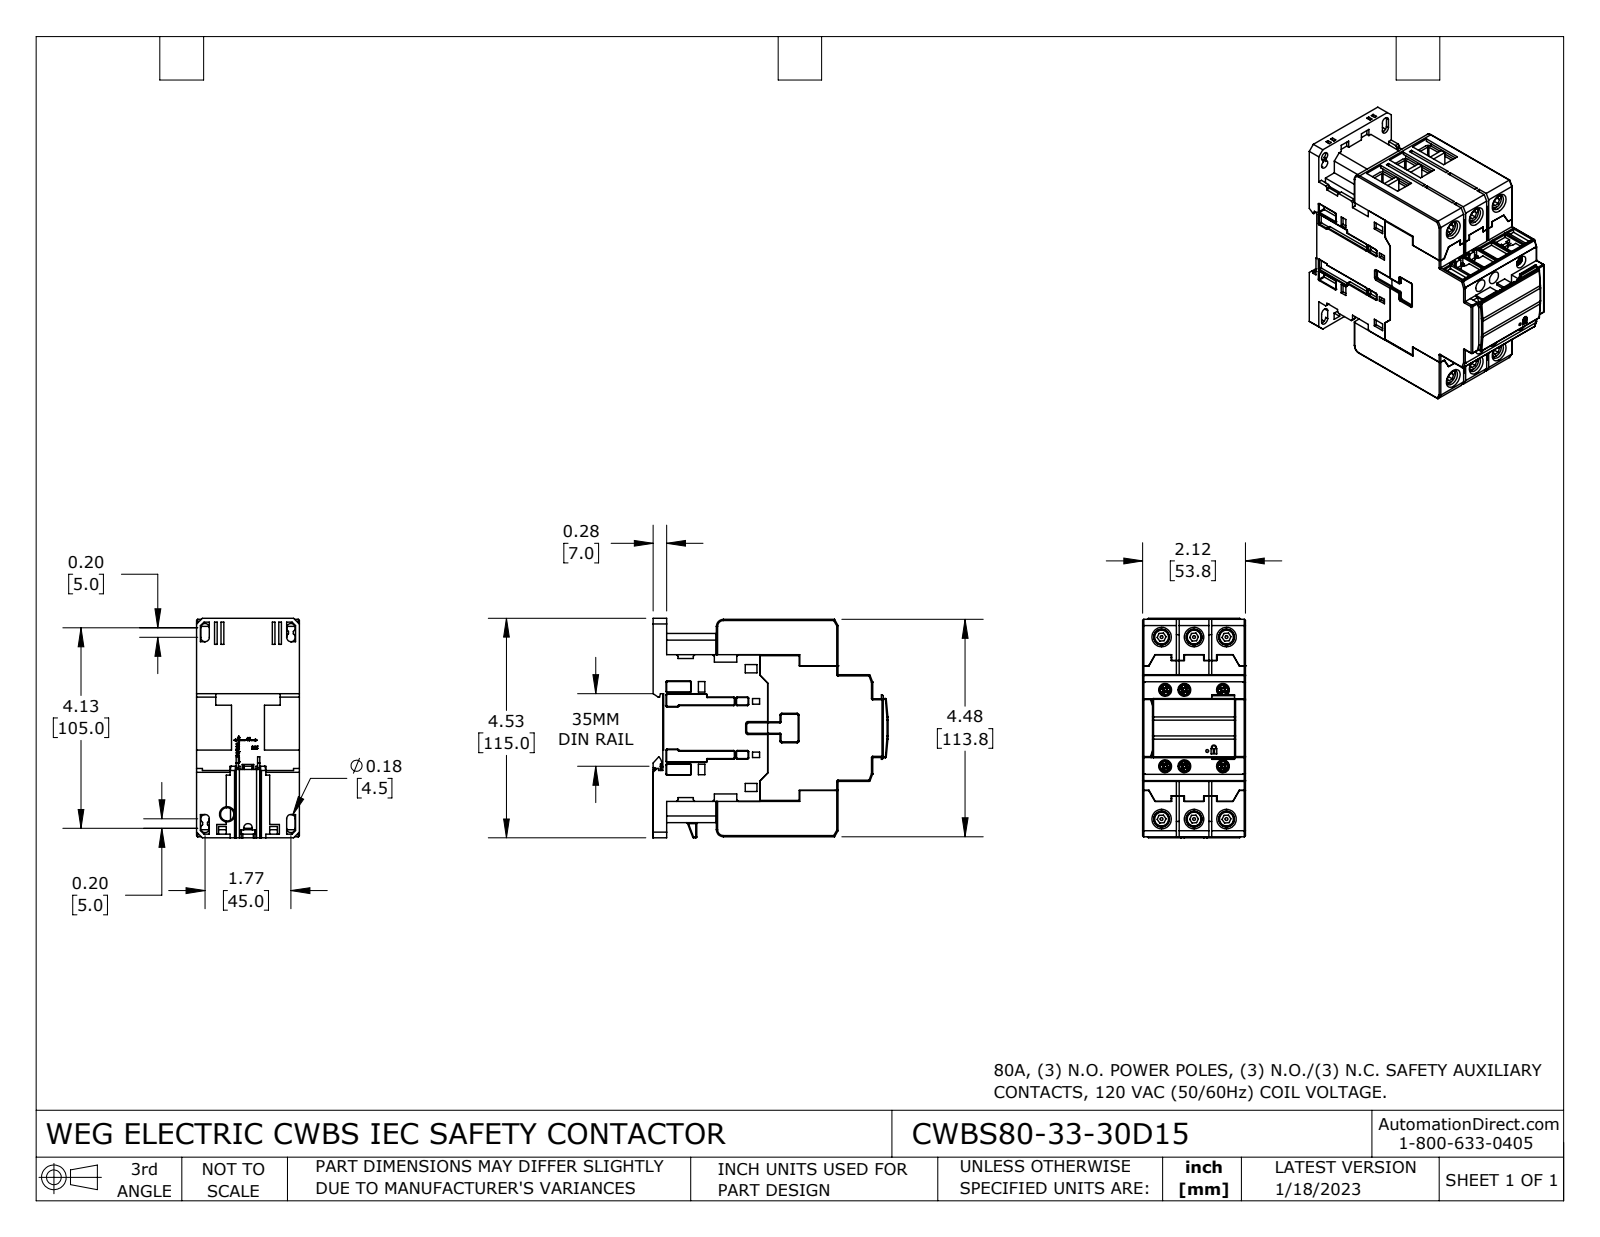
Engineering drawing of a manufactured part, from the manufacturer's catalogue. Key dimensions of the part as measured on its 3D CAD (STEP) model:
Part name (STEP PRODUCT): CWBS80-33-30D15
STEP written by: SolidWorks 2021 (CONFIG_CONTROL_DESIGN)
Units: inches
Bodies: 37 solids, 2637 faces (1669 planar, 550 cylindrical, 418 other)
Overall size (bounding box): 4.846 × 4.528 × 2.118
Volume: 33.67 in³ · Surface area: 209.3 in²
Round holes (diameter × count): ⌀0.124 ×6, ⌀0.197 ×6, ⌀0.264 ×6, ⌀0.323 ×6, ⌀0.177 ×4, ⌀0.125 ×2, ⌀0.276 ×2, ⌀0.059 ×1
Round bosses / shafts (diameter × count): ⌀0.343 ×6, ⌀0.236 ×6, ⌀0.135 ×6
Partial cylindrical surfaces — rounded edges, fillets, slot ends (radius × count): R0.02 ×89, R0.012 ×69, R0.004 ×48, R0.024 ×42, R0.079 ×18, R0.089 ×5, R0.039 ×3, R0.059 ×3
Main face-to-face distances: 0.059, 2.118, 0.669, 0.728, 3.024, 3.752, 0.108, 0.217, 3.811, 0.098
Hole centre spacings: 0.669, 1.091, 1.241, 1.669, 2.665, 2.73, 2.949, 3.811
